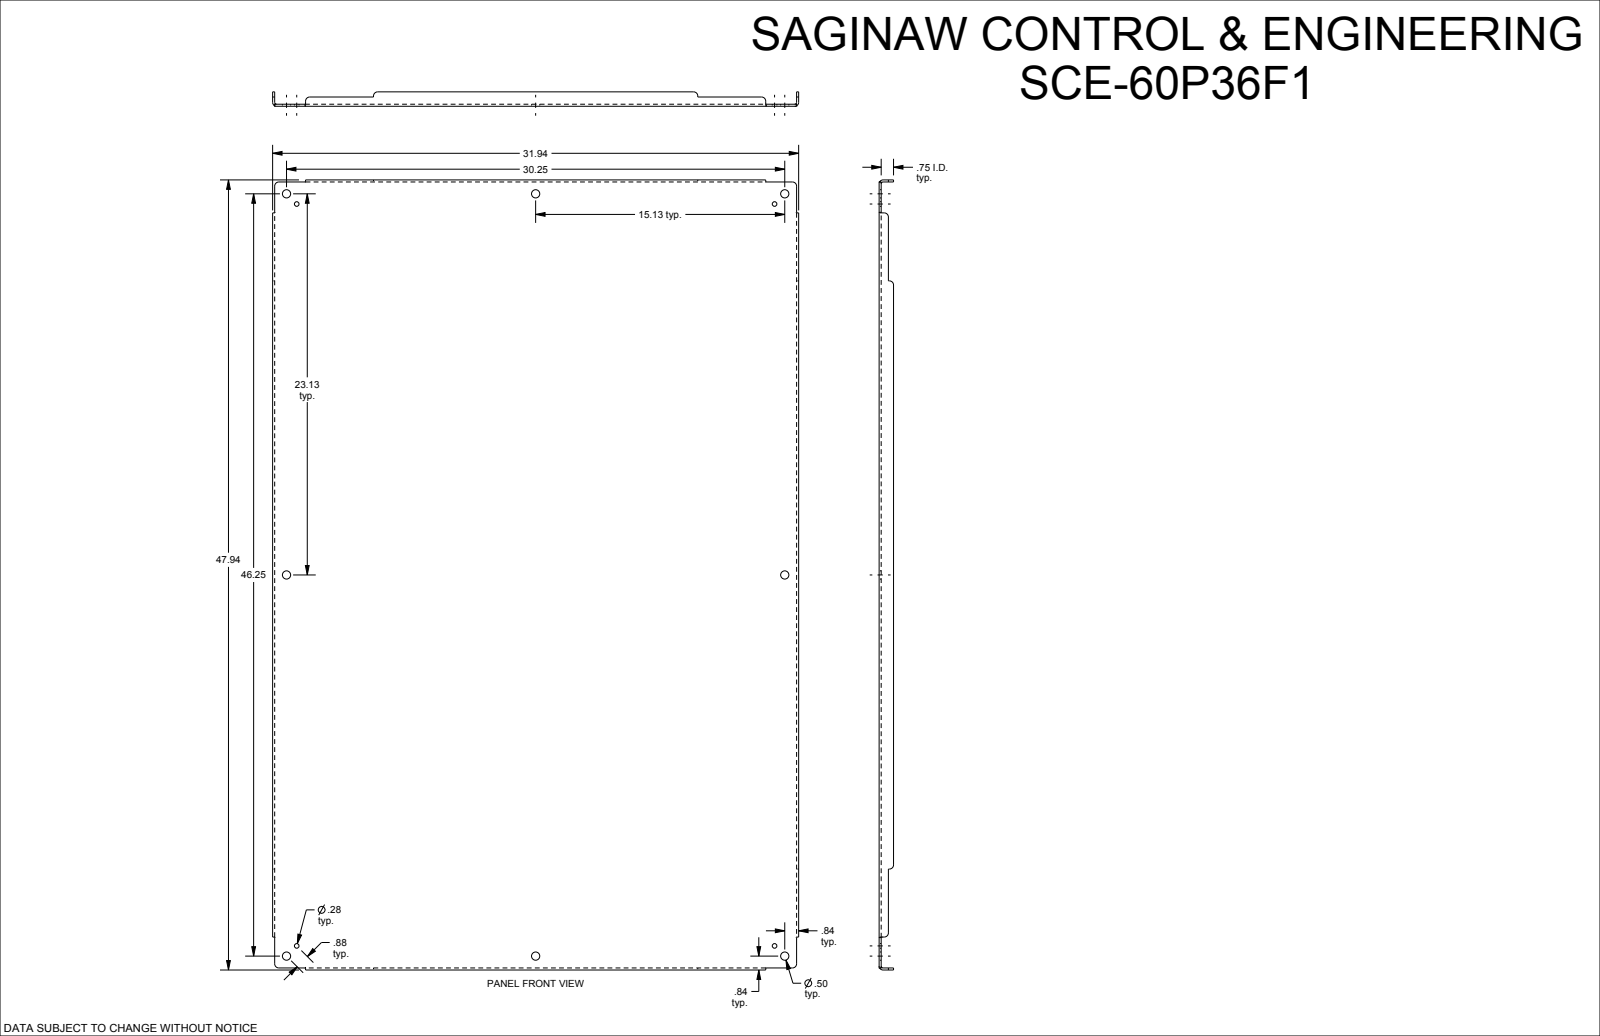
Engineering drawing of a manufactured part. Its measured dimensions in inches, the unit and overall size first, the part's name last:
Units: inches
Overall size (bounding box): 47.938 × 31.938 × 0.875
Round holes (diameter × count): ⌀0.5 ×8, ⌀0.281 ×4
Partial cylindrical surfaces — rounded edges, fillets, slot ends (radius × count): R0.25 ×12, R0.112 ×4, R0.237 ×4
Main face-to-face distances: 0.125, 0.125, 31.813, 47.813, 31.687, 31.938, 47.687, 47.938, 0.75, 0.875
Hole centre spacings: 0.875, 14.52, 15.125, 22.515, 23.125, 27.632, 29.637, 37.209
Volume: 201.7 in³ · Surface area: 3 250 in²
Bodies: 1 solid, 110 faces (46 planar, 40 cylindrical, 24 other)
Part name (STEP PRODUCT): SCE-60P36F1
STEP written by: SolidWorks 2019 (CONFIG_CONTROL_DESIGN)
